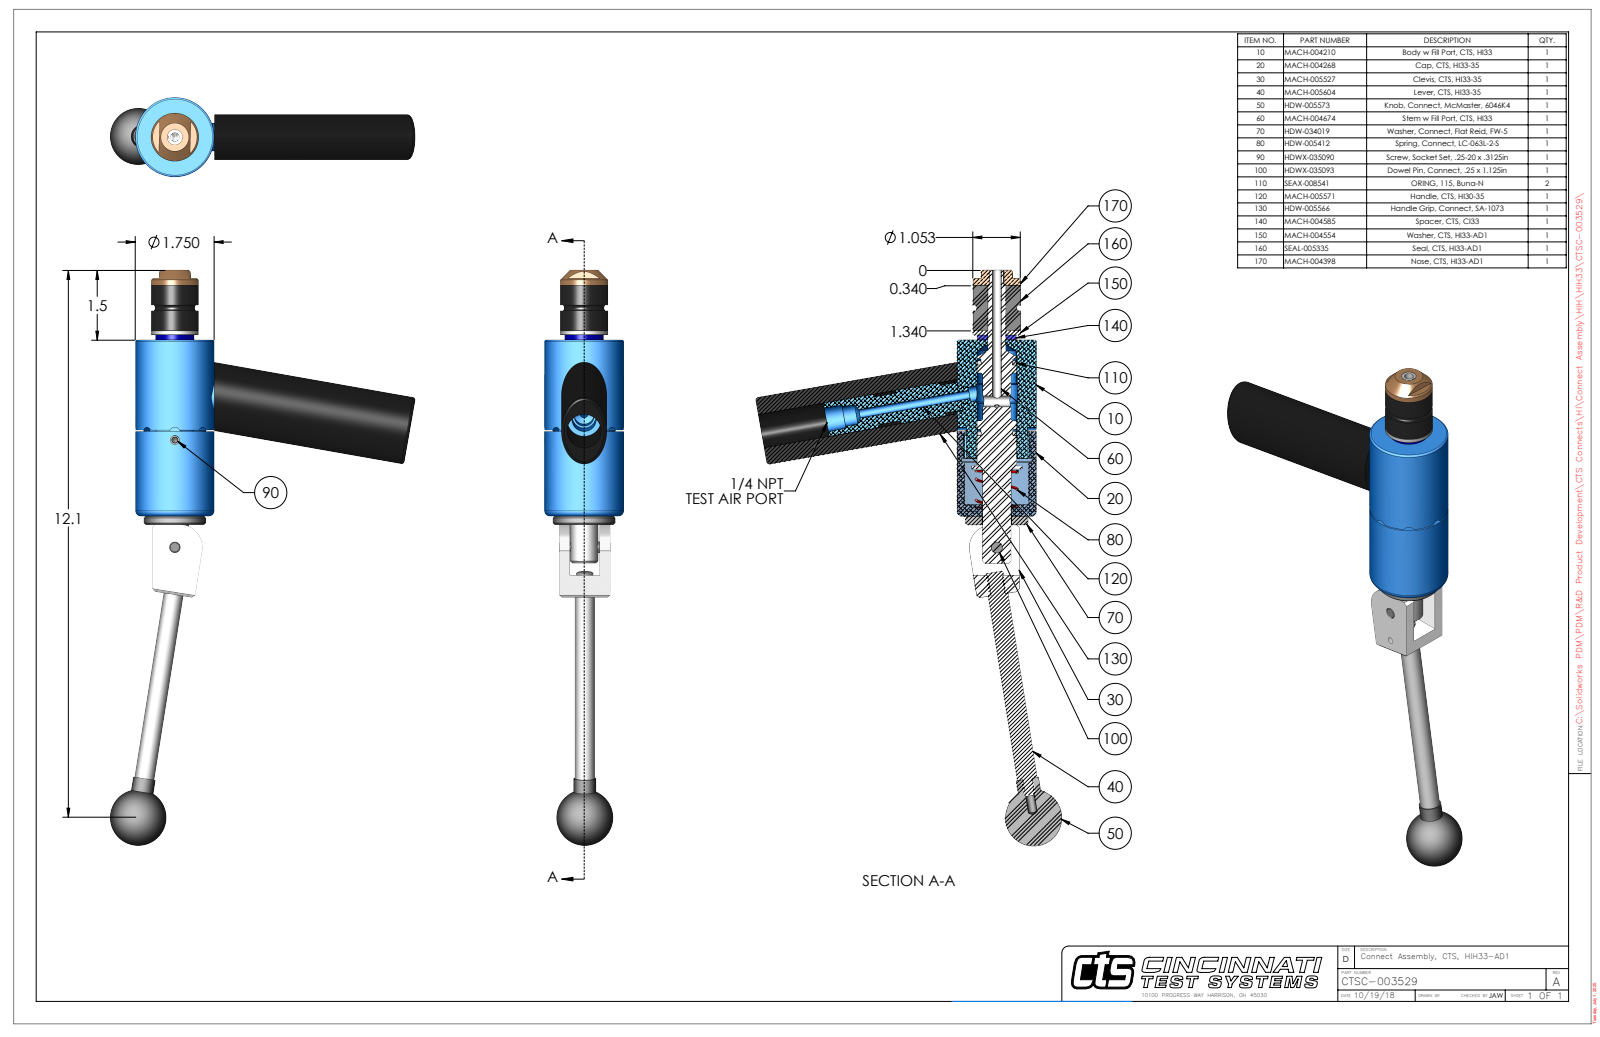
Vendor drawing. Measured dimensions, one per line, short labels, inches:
name: CTSC-003529
written by: SolidWorks 2023 (AUTOMOTIVE_DESIGN)
unit: in
bodies: 11 solids, 288 faces (93 planar, 126 cylindrical, 69 other)
size: 12.751 × 6.763 × 1.75
volume: 17.96 in³; area: 112.8 in²
holes: 2× ⌀0.201, 2× ⌀0.313, 1× ⌀0.15, 1× ⌀0.187, 1× ⌀0.204, 1× ⌀0.249, 1× ⌀0.25, 1× ⌀0.251, 1× ⌀0.39, 1× ⌀0.397, 1× ⌀0.403, 1× ⌀0.438
bosses: 2× ⌀0.375, 2× ⌀0.312, 2× ⌀0.25, 1× ⌀1.75, 1× ⌀1.38, 1× ⌀1.053, 1× ⌀0.858, 1× ⌀0.75
rounds: 4× R0.125, 2× R0.029, 1× R0.149, 1× R0.33, 1× R0.5, 1× R0.695, 1× R0.824
face distances: 3.907, 1.207, 5.114, 1, 1.12, 0.207, 4.114, 5.302, 4.302, 4.095
hole spacings: 0.74, 2.376, 3.116
